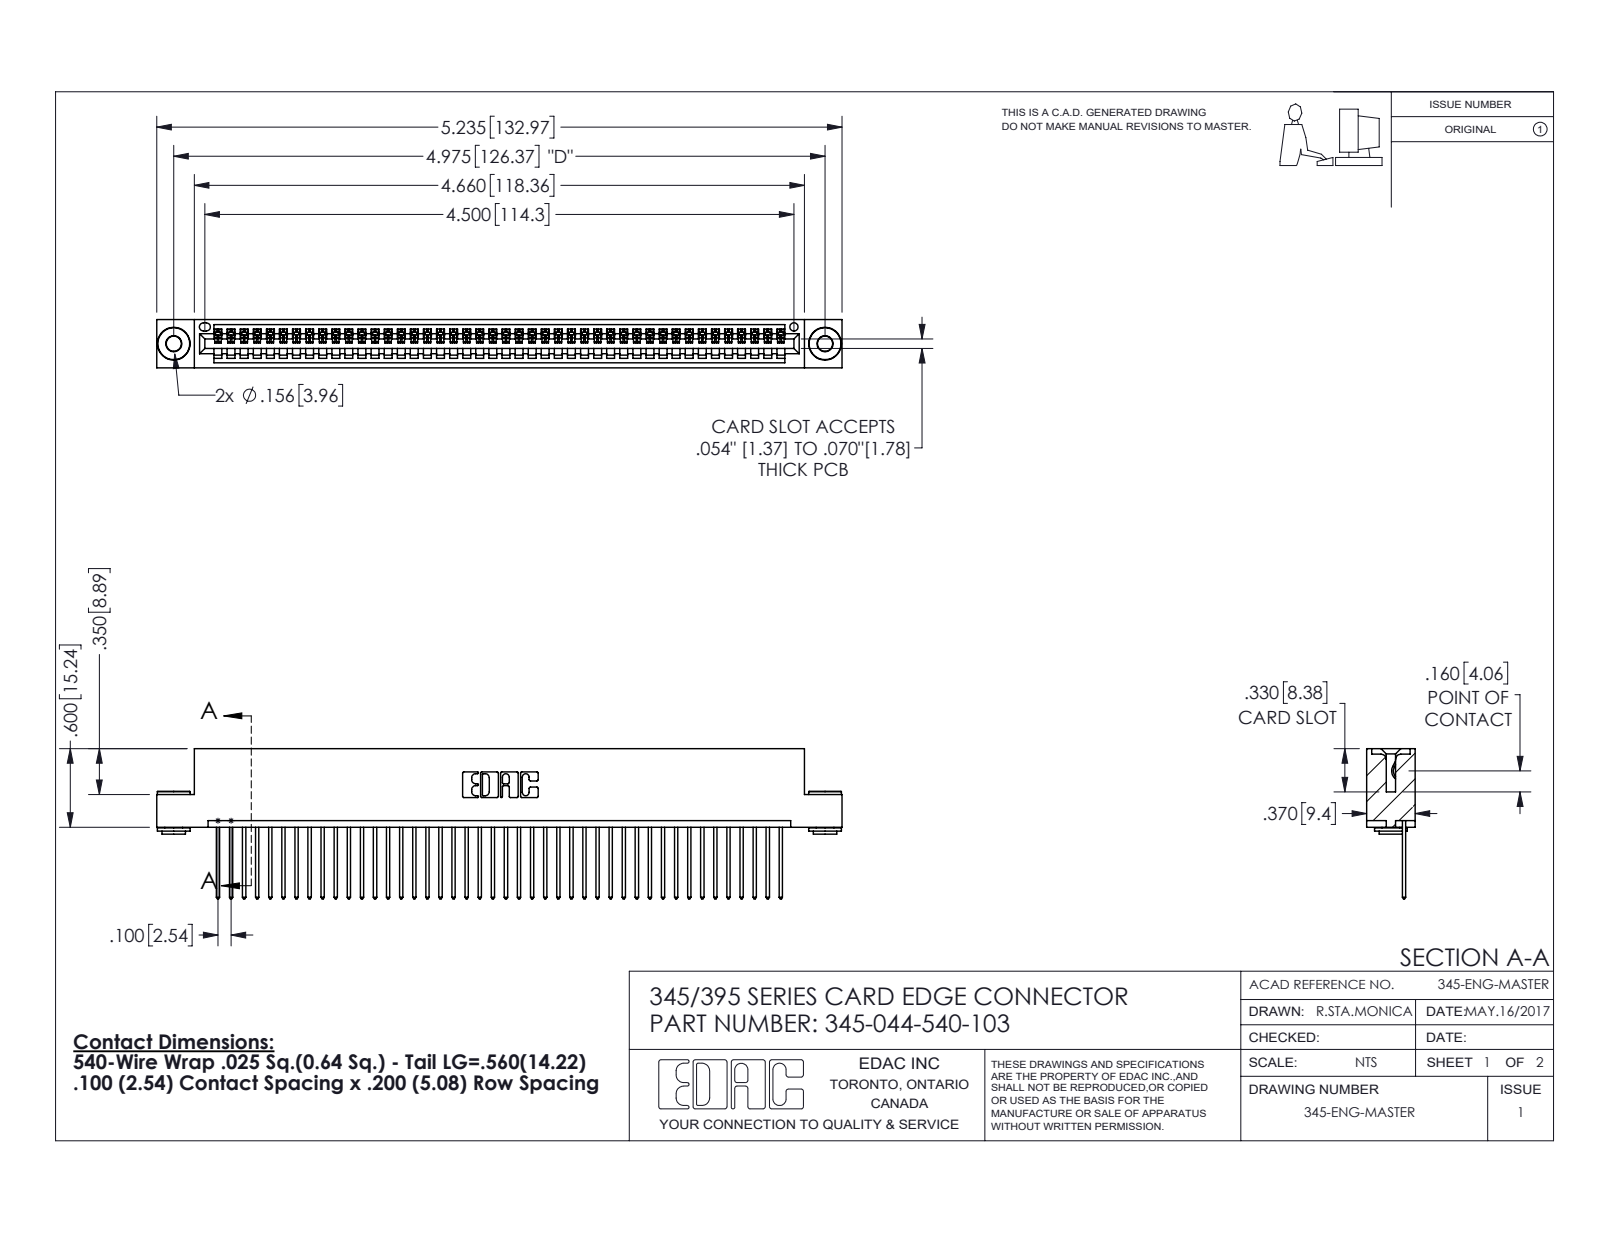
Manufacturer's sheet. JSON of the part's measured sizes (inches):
{"part_name": "345-292-001_345-293-140; 345 Part_Flush Mounting Lugs - 0.156 Dia-TH; 345-044-540-103; 345-250-002_345-250-002-102", "step_written_by": "SolidWorks 2016 (CONFIG_CONTROL_DESIGN)", "units": "inches", "bodies": {"solids": 47, "faces": 2716, "planar": 1850, "cylindrical": 858, "other": 8}, "overall_size": [5.235, 1.147, 0.37], "volume_in3": 0.777, "surface_area_in2": 27.25, "round_holes": [[0.116, 2], [0.156, 2], [0.064, 1]], "round_bosses_or_shafts": [[0.25, 2], [0.18, 2], [0.136, 2]], "partial_cylinders_radius": [[0.006, 88], [0.01, 88], [0.01, 22], [0.007, 6], [0.031, 6], [0.026, 3], [0.031, 2], [0.04, 2]], "face_to_face_distances": [0.072, 0.298, 0.37, 0.025, 0.2, 0.098, 0.272, 0.225, 0.149, 0.072], "hole_center_spacings": [0.27, 4.739, 4.975]}
